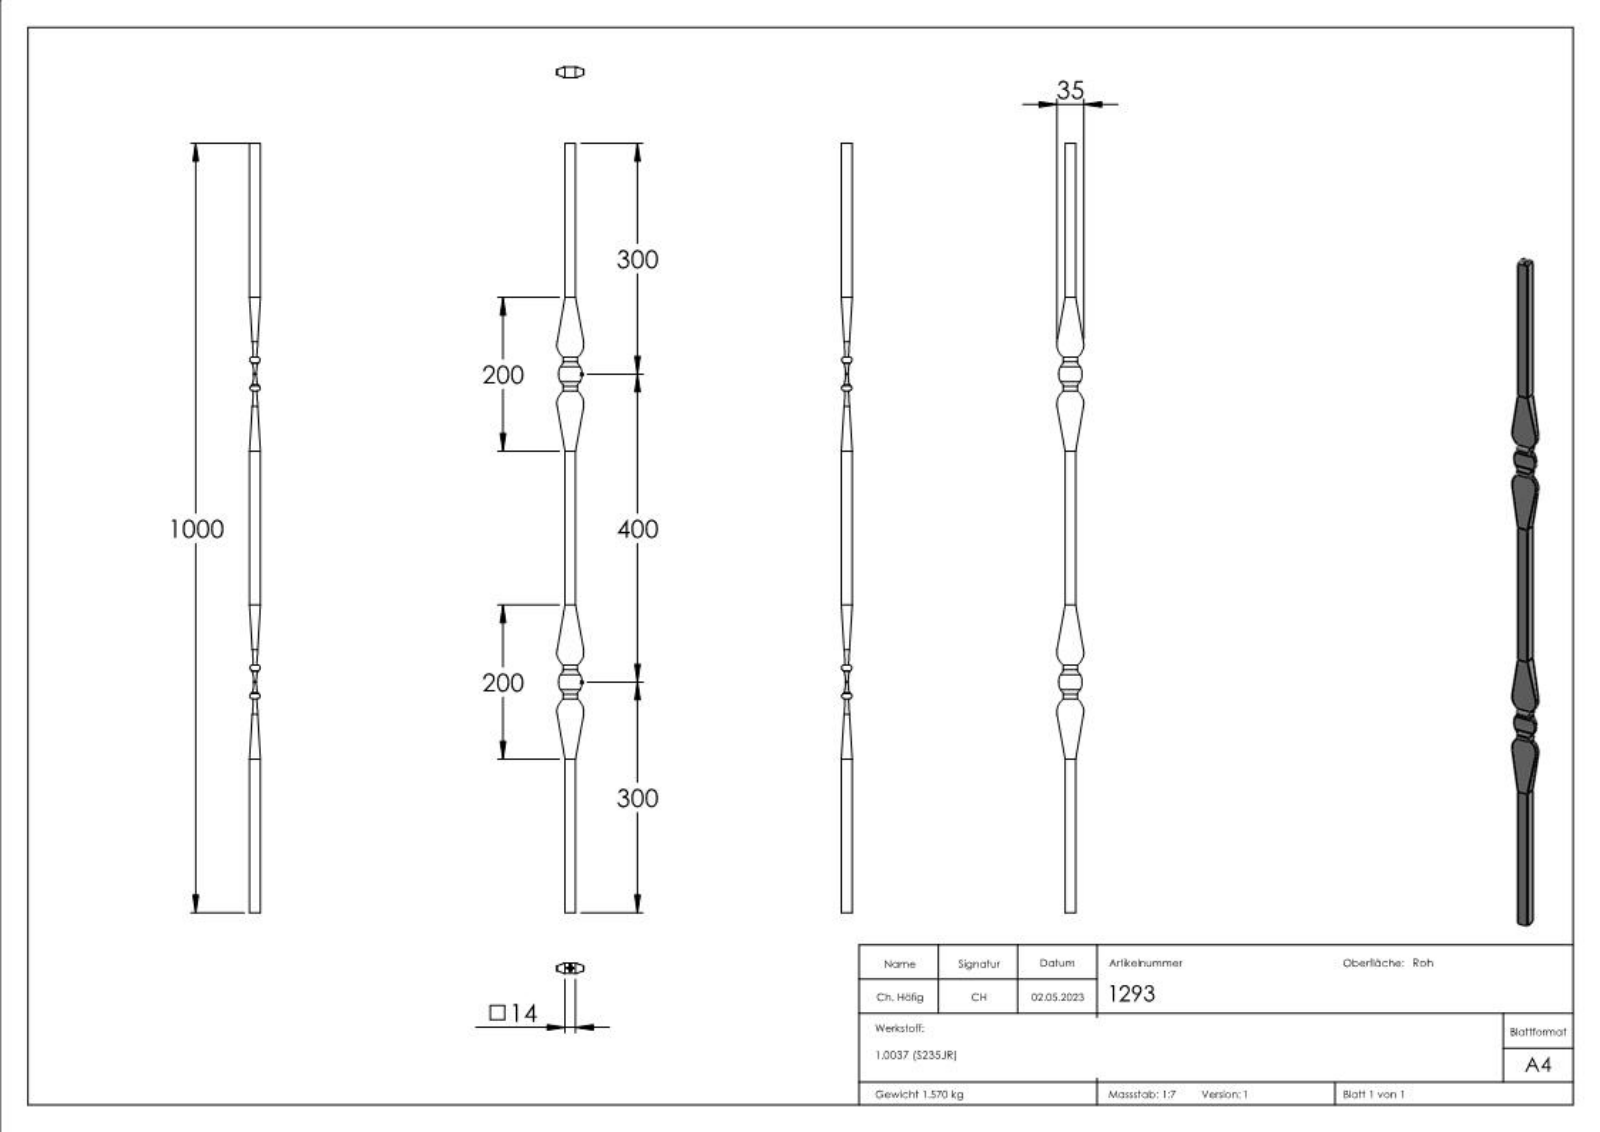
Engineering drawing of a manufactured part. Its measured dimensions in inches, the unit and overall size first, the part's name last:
Units: inches
Overall size (bounding box): 39.37 × 1.378 × 0.551
Partial cylindrical surfaces — rounded edges, fillets, slot ends (radius × count): R0.077 ×8, R0.138 ×8, R0.394 ×8, R0.709 ×8, R0.797 ×8, R2.982 ×4
Main face-to-face distances: 0.551, 0.07, 0.961, 1.031, 0.891, 1.905, 2.724, 4.629, 0.82, 0.079
Volume: 12.28 in³ · Surface area: 96.51 in²
Bodies: 1 solid, 302 faces (161 planar, 44 cylindrical, 97 other)
Part name (STEP PRODUCT): 1293
STEP written by: SolidWorks 2018 (CONFIG_CONTROL_DESIGN)
